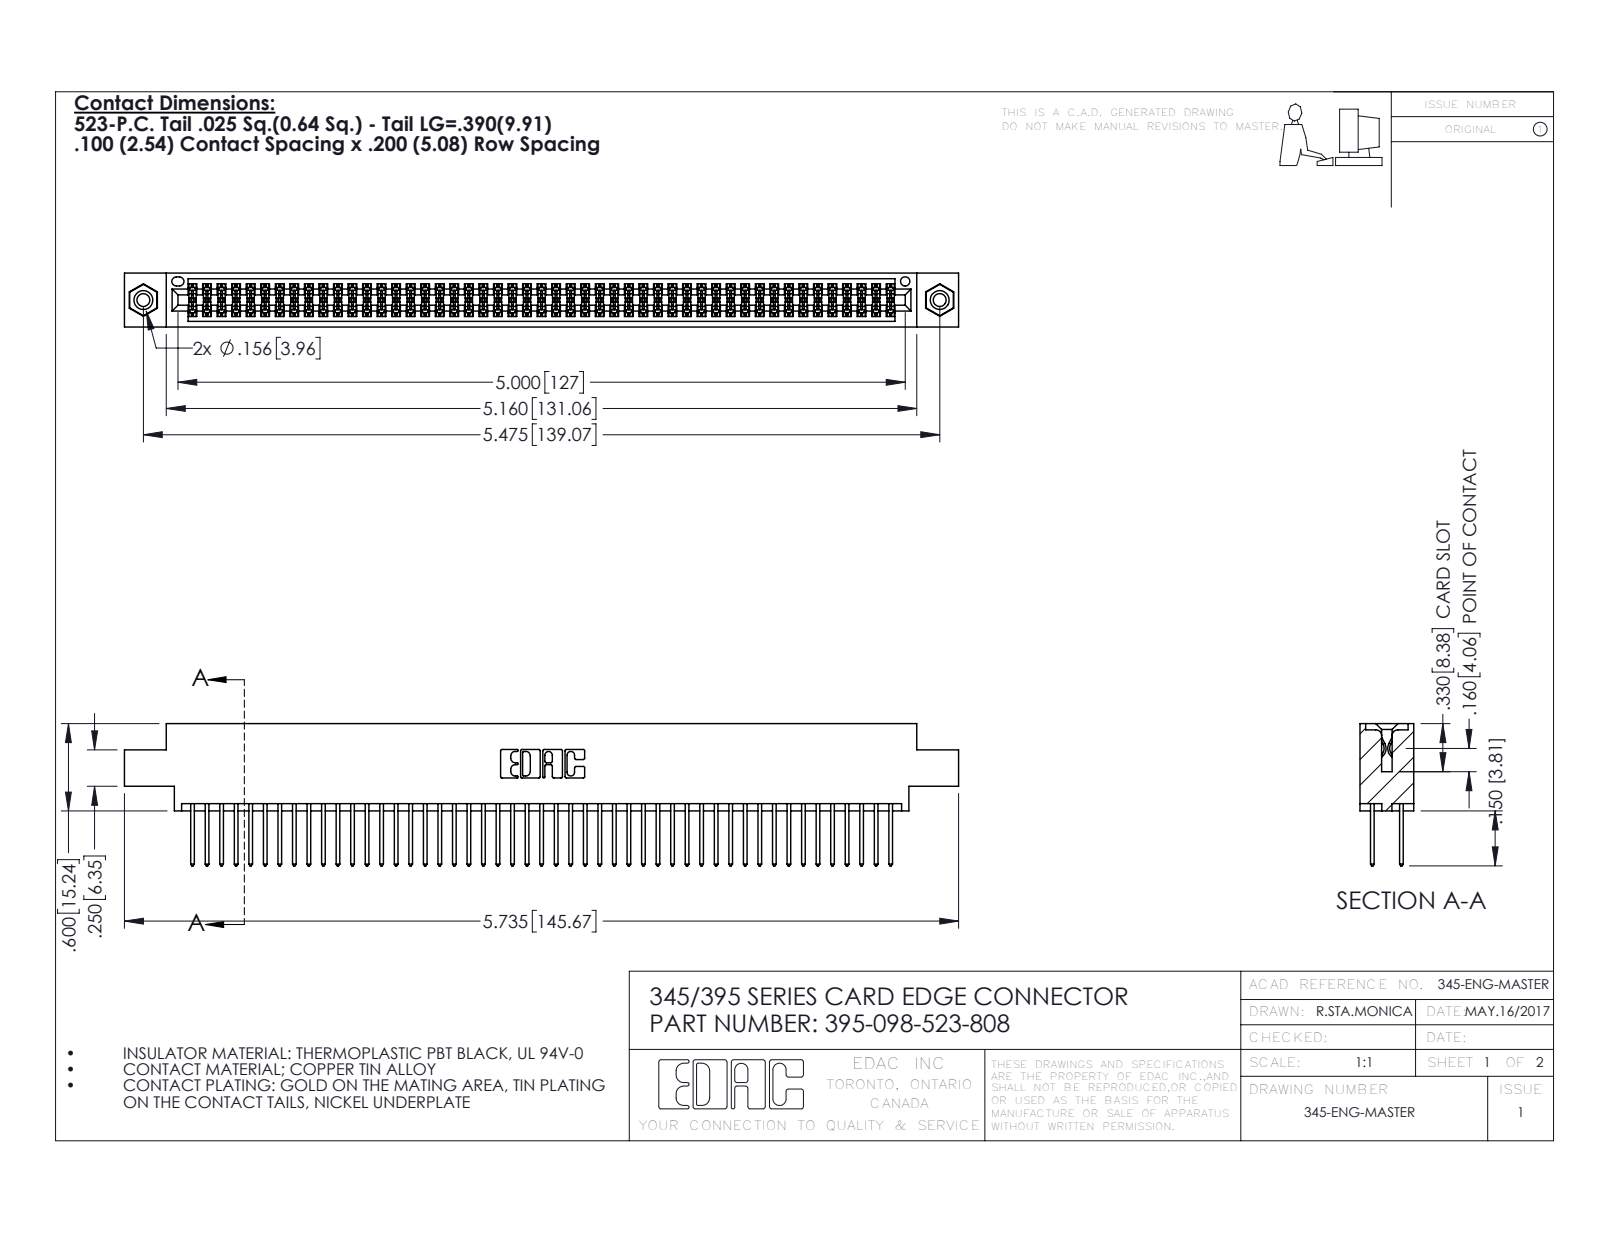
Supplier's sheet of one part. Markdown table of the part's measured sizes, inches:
| quantity | value |
| --- | --- |
| part name | 345-292-001_345-293-123; 345 Part_0.170 Offset - 0.156 Dia-TI; 395-098-523-808; 345-250-001_345-250-003-102 |
| STEP written by | SolidWorks 2016 (CONFIG_CONTROL_DESIGN) |
| units | inches |
| bodies | 101 solids, 5090 faces (3350 planar, 1724 cylindrical, 16 other) |
| overall size | 5.735 × 0.977 × 0.37 |
| volume | 0.872 in³ |
| surface area | 34.61 in² |
| round holes (diameter × count) | 0.089 × 2, 0.125 × 2, 0.156 × 2, 0.064 × 1 |
| round bosses / shafts (diameter × count) | 0.155 × 2 |
| partial cylindrical surfaces (radius × count) | 0.006 × 147, 0.01 × 98, 0.01 × 22, 0.007 × 6, 0.031 × 6, 0.026 × 3, 0.014 × 2, 0.019 × 2 |
| main face-to-face distances | 0.072, 0.298, 0.2, 0.098, 0.272, 0.025, 0.37, 0.225, 0.175, 0.149 |
| hole center spacings | 0.27, 5.239, 5.475 |
